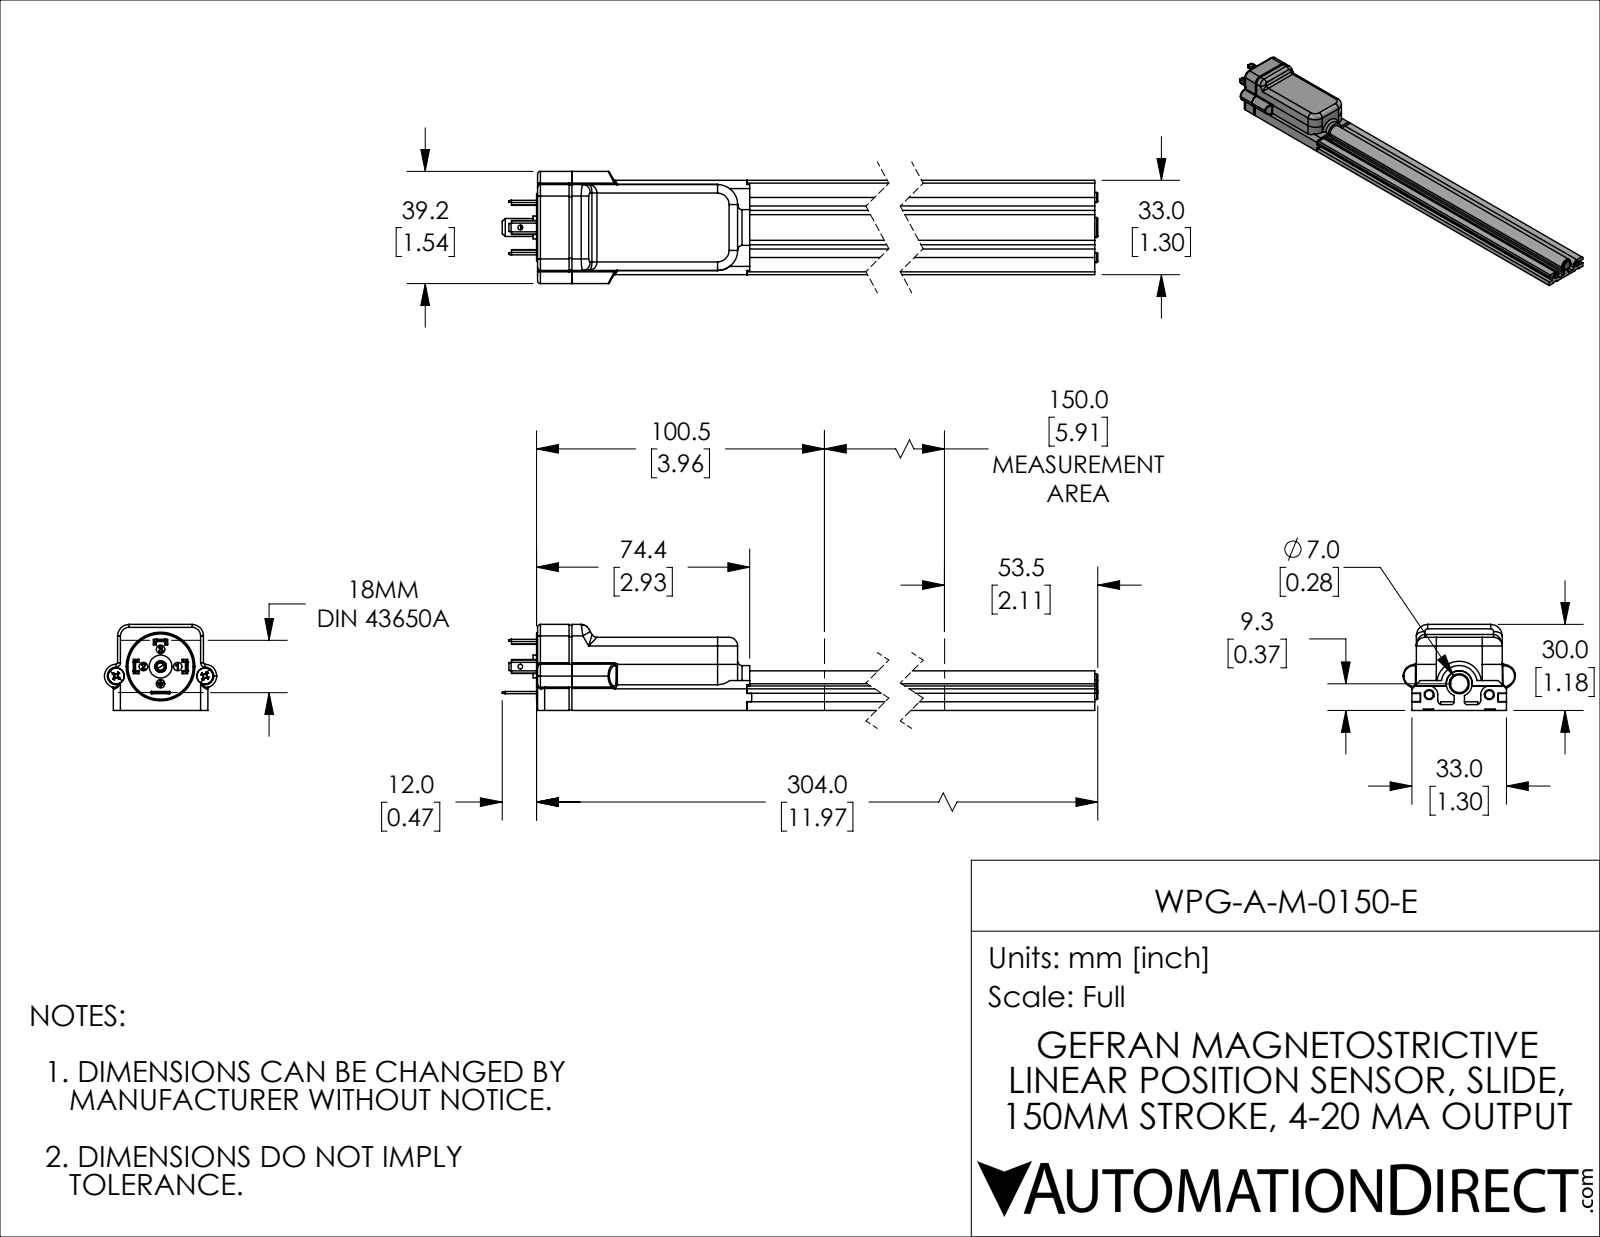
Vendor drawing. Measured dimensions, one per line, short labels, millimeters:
name: WPG-A-M-0150-E
written by: SolidWorks 2021 (CONFIG_CONTROL_DESIGN)
unit: mm
bodies: 15 solids, 589 faces (371 planar, 139 cylindrical, 79 other)
size: 316 × 39.2 × 30
volume: 113 345 mm³; area: 47 485 mm²
holes: 5× ⌀3, 2× ⌀1.5, 2× ⌀1.65, 2× ⌀3.2, 2× ⌀5.7, 1× ⌀1.6, 1× ⌀2.5, 1× ⌀4
bosses: 2× ⌀5.6, 2× ⌀3.5, 2× ⌀2.85, 1× ⌀9, 1× ⌀8, 1× ⌀7, 1× ⌀5.3, 1× ⌀3.94
rounds: 8× R0.5, 8× R3, 6× R0.85, 5× R1, 4× R0.8, 4× R1.5, 4× R4.1, 4× R7
face distances: 3, 1, 1.5, 2.5, 5.5, 6, 8.5, 22.5, 30, 0.5
hole spacings: 6, 8.49, 10.06, 12, 12.3, 15.73, 15.85, 18.08
